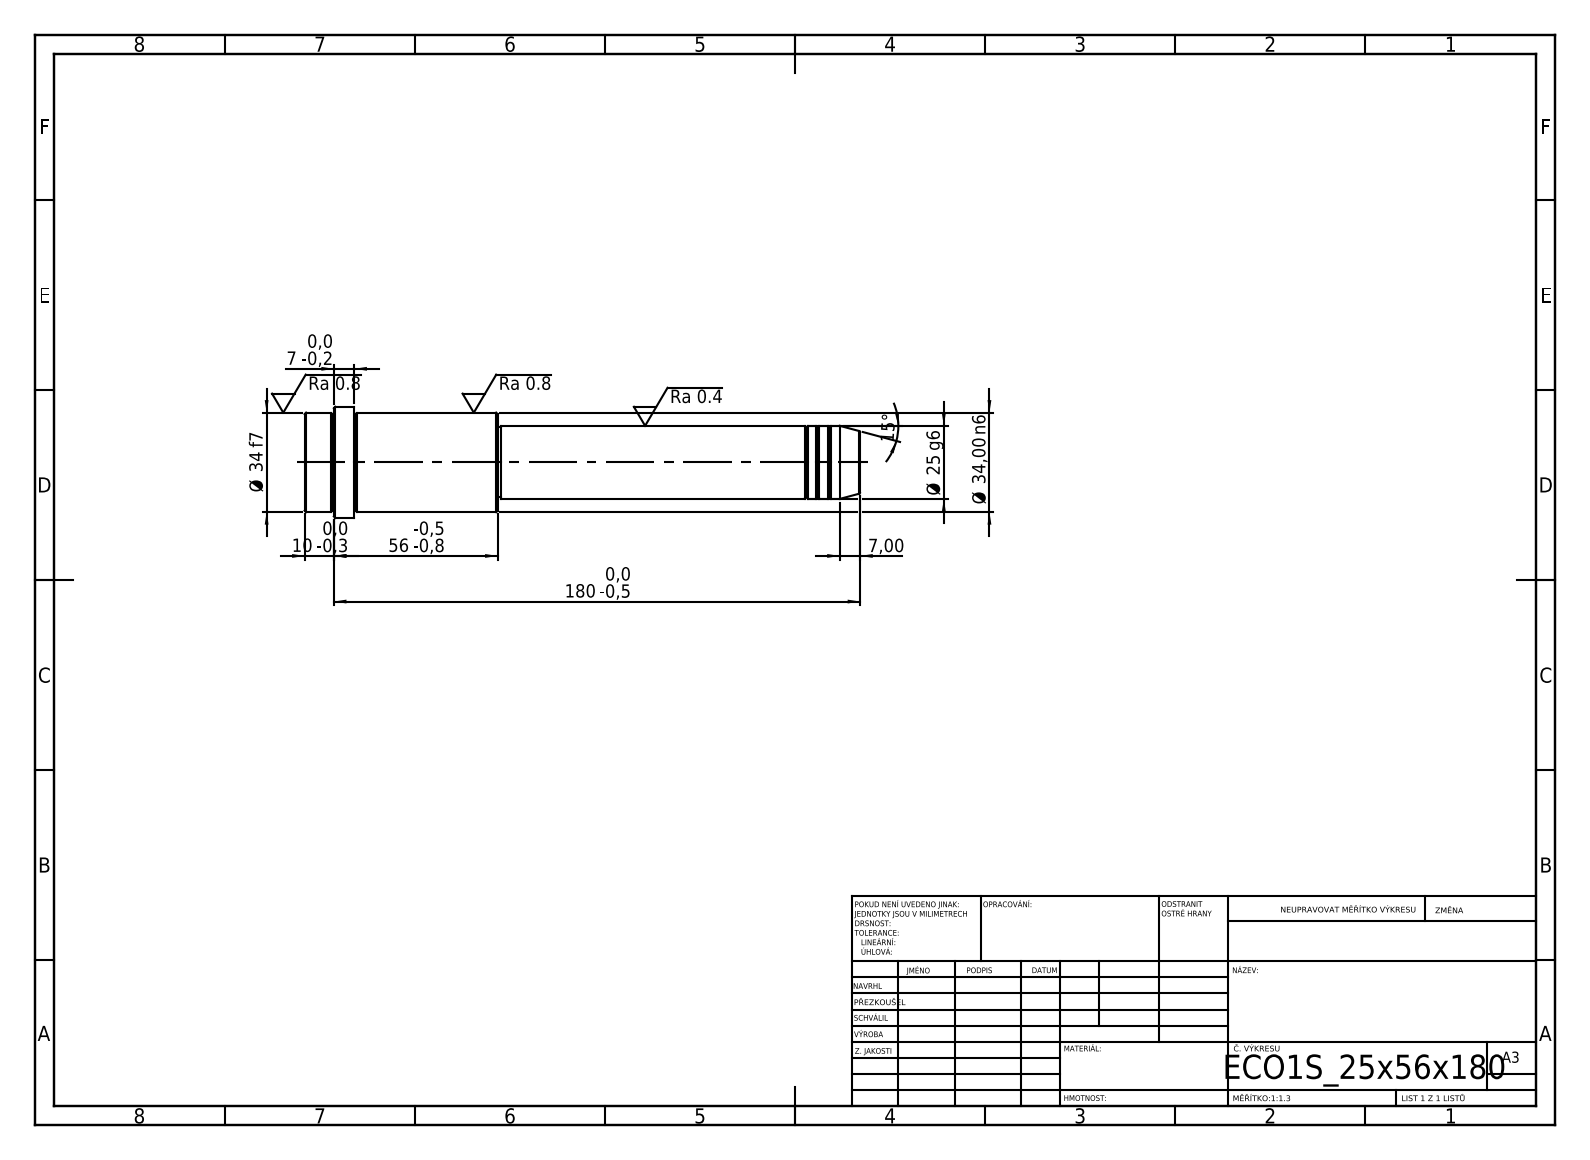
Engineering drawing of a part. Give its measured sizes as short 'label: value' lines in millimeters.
written by: SolidWorks 2019 (CONFIG_CONTROL_DESIGN)
unit: mm
bodies: 1 solid, 52 faces (6 planar, 16 cylindrical, 30 other)
size: 190 × 38 × 38
volume: 121 629 mm³; area: 19 194 mm²
bosses: 1× ⌀38, 1× ⌀34, 1× ⌀25, 1× ⌀24
face distances: 66, 124, 190, 173, 49, 17, 180, 56, 7, 10
